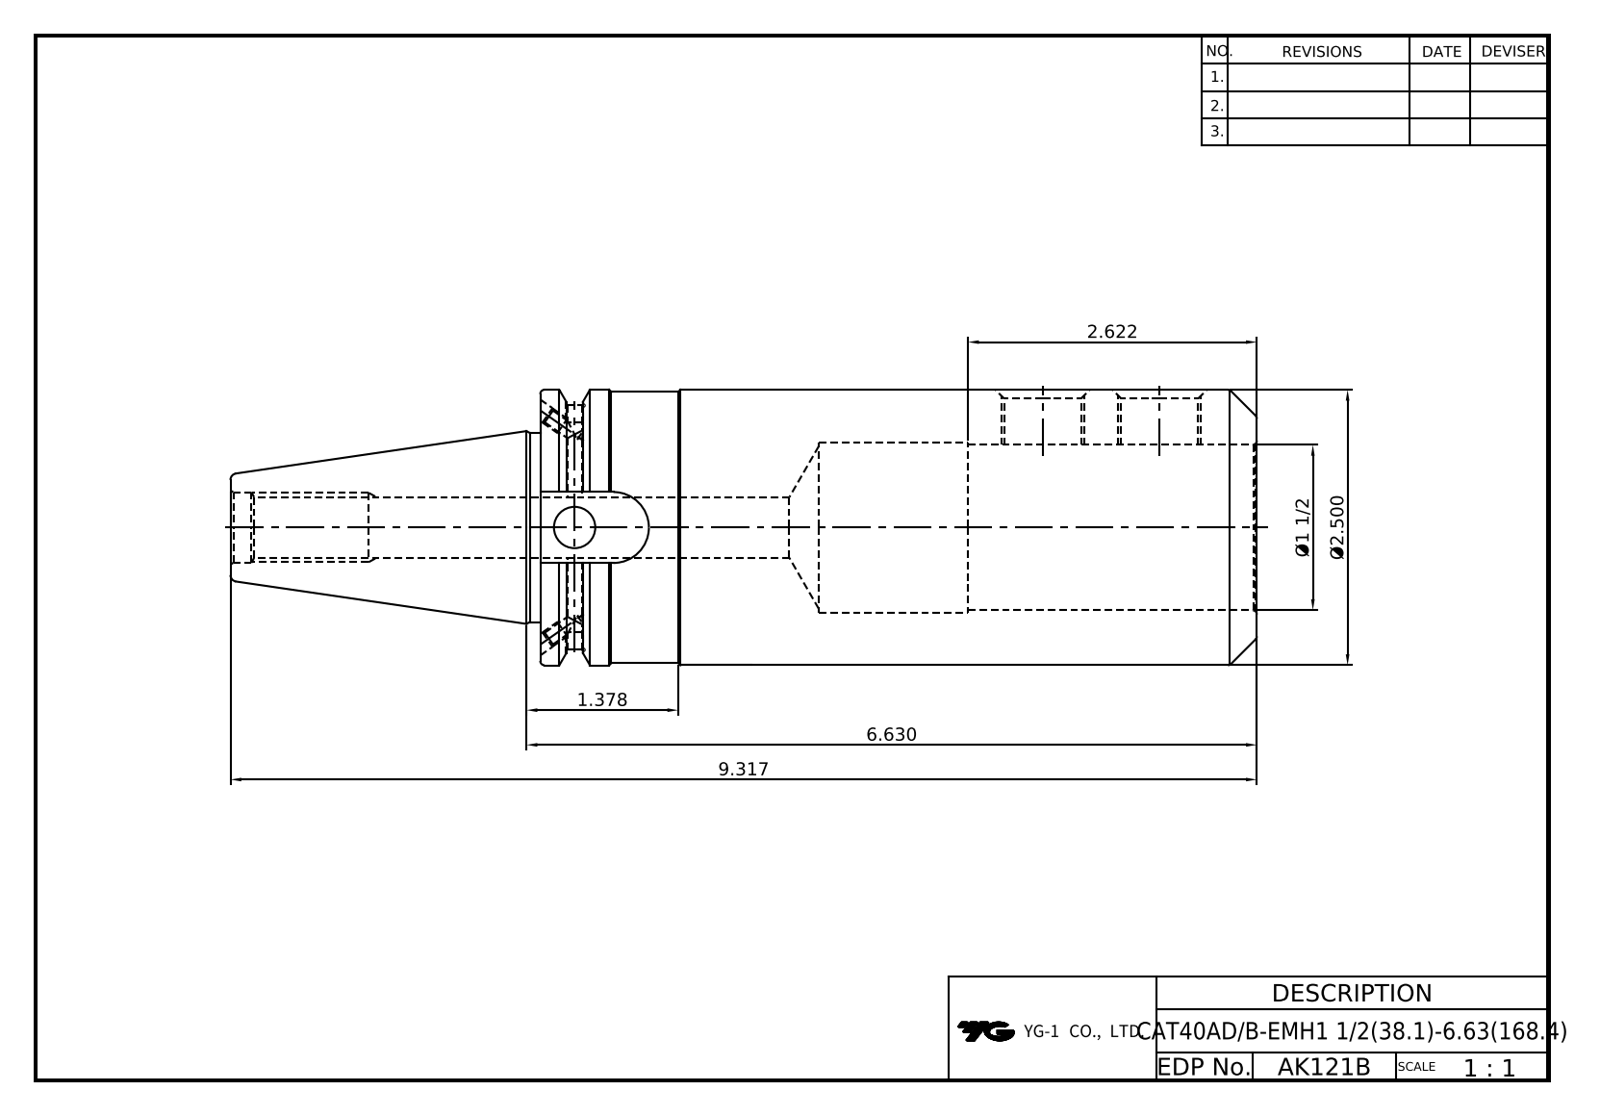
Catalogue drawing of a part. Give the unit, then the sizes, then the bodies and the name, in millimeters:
Units: millimetres
Overall size (bounding box): 236.65 × 63.5 × 63.5
Round holes (diameter × count): ⌀3.24 ×4, ⌀4 ×2, ⌀4.2 ×2, ⌀17.32 ×2, ⌀9.53 ×1, ⌀13.39 ×1, ⌀16.3 ×1, ⌀38.1 ×1, ⌀39.3 ×1
Round bosses / shafts (diameter × count): ⌀63.5 ×1, ⌀62.5 ×1, ⌀43.6 ×1
Partial cylindrical surfaces — rounded edges, fillets, slot ends (radius × count): R8.19 ×1, R28.15 ×1
Main face-to-face distances: 64.23, 165.23, 101, 47.6, 16.38, 71.42, 135.65, 236.65, 81.29, 9.87
Hole centre spacings: 27
Volume: 434 971 mm³ · Surface area: 65 275 mm²
Bodies: 1 solid, 92 faces (34 planar, 32 cylindrical, 26 other)
Part name (STEP PRODUCT): LO-CAT40ADB-EMH38.1-168.4
STEP written by: Autodesk Inventor 2025 (AUTOMOTIVE_DESIGN)
